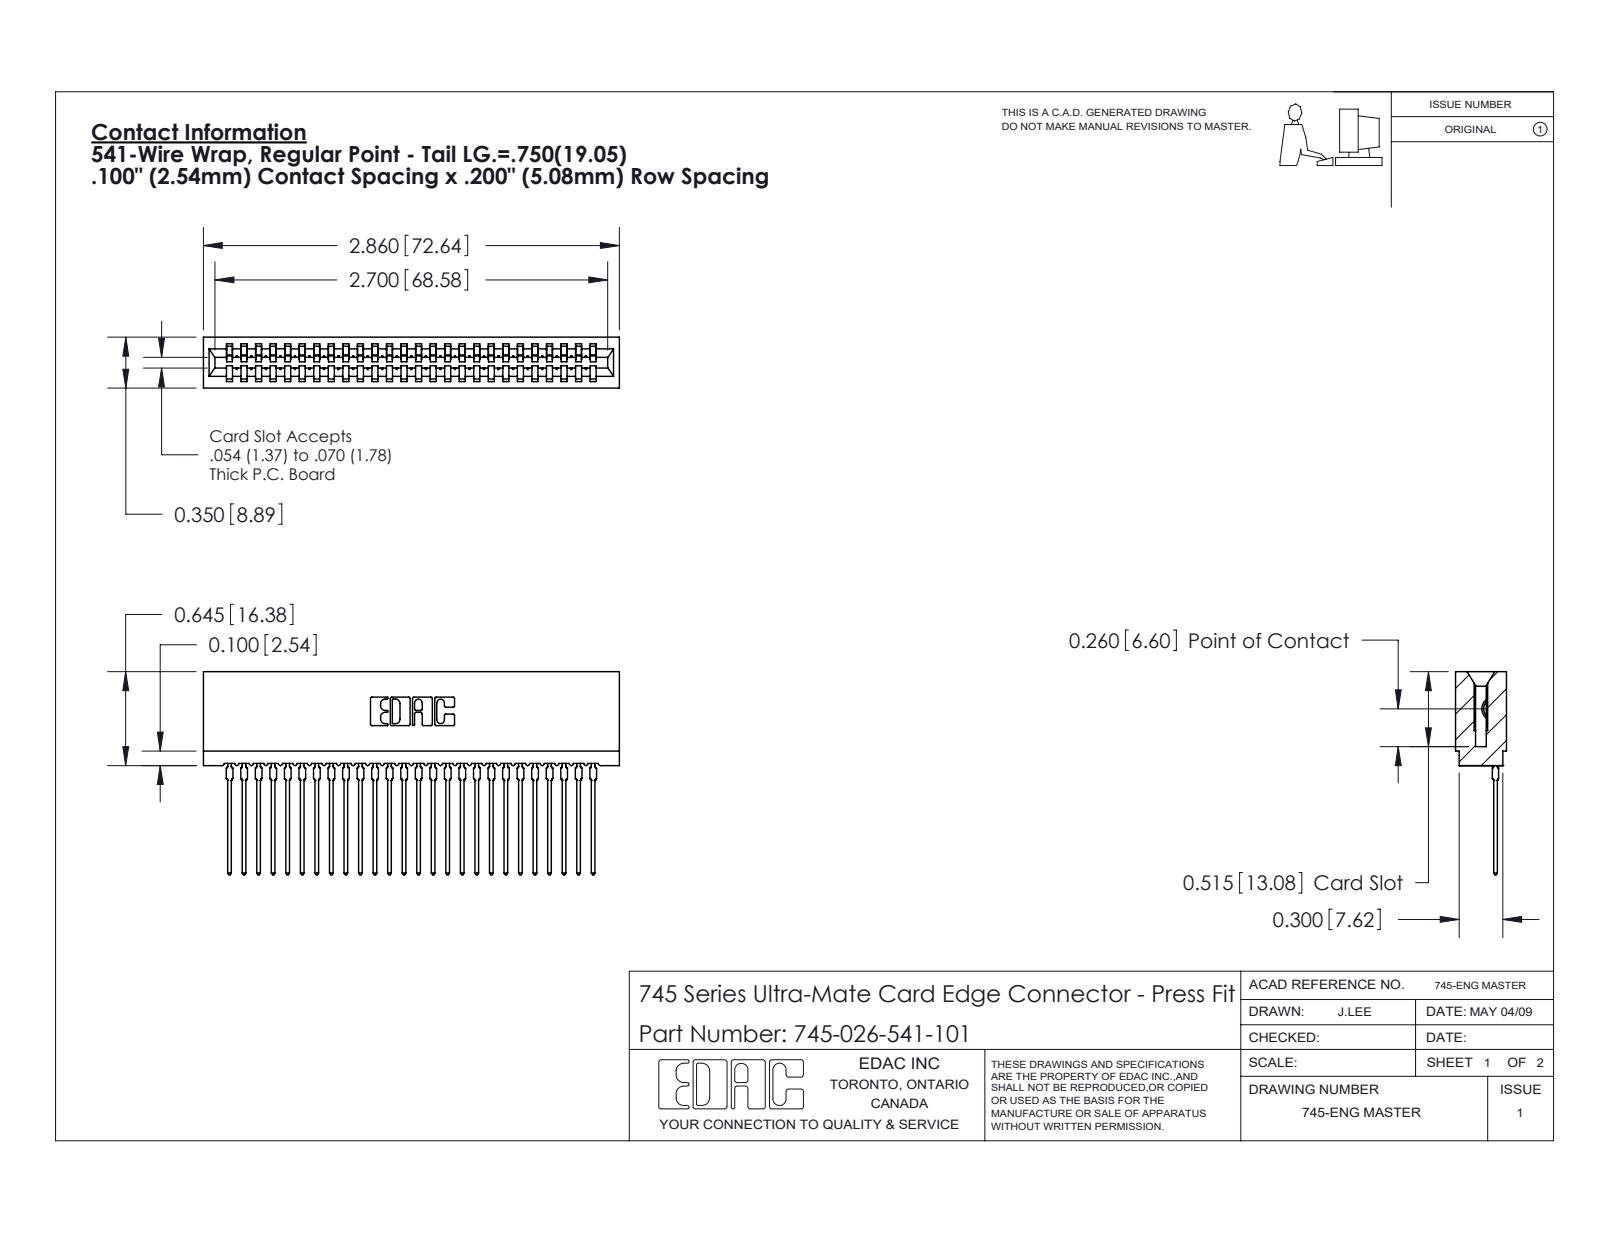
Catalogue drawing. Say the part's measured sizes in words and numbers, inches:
The part is named "745-292-001_541; 745 Part_Insulator Option - 01; 745-026-541-101". Its 3-D file was written by "SolidWorks 2020 (CONFIG_CONTROL_DESIGN)". It is 27 solids with 3007 faces: 1797 planar, 534 cylindrical and 676 other. Overall it measures 2.86 by 1.396 by 0.35 inches. Its volume is 0.397 cubic inches and its surface area 19.11 square inches. Partial cylindrical surfaces (rounded edges, fillets, slot ends): 52 of radius 0.015, 52 of radius 0.021, 22 of radius 0.01, 6 of radius 0.007, 6 of radius 0.031, 4 of radius 0.005, 4 of radius 0.011, 3 of radius 0.026. The main face-to-face distances are 0.35, 0.1, 0.2, 0.3, 0.138, 0.212, 0.063, 0.287, 0.045, 0.305.
